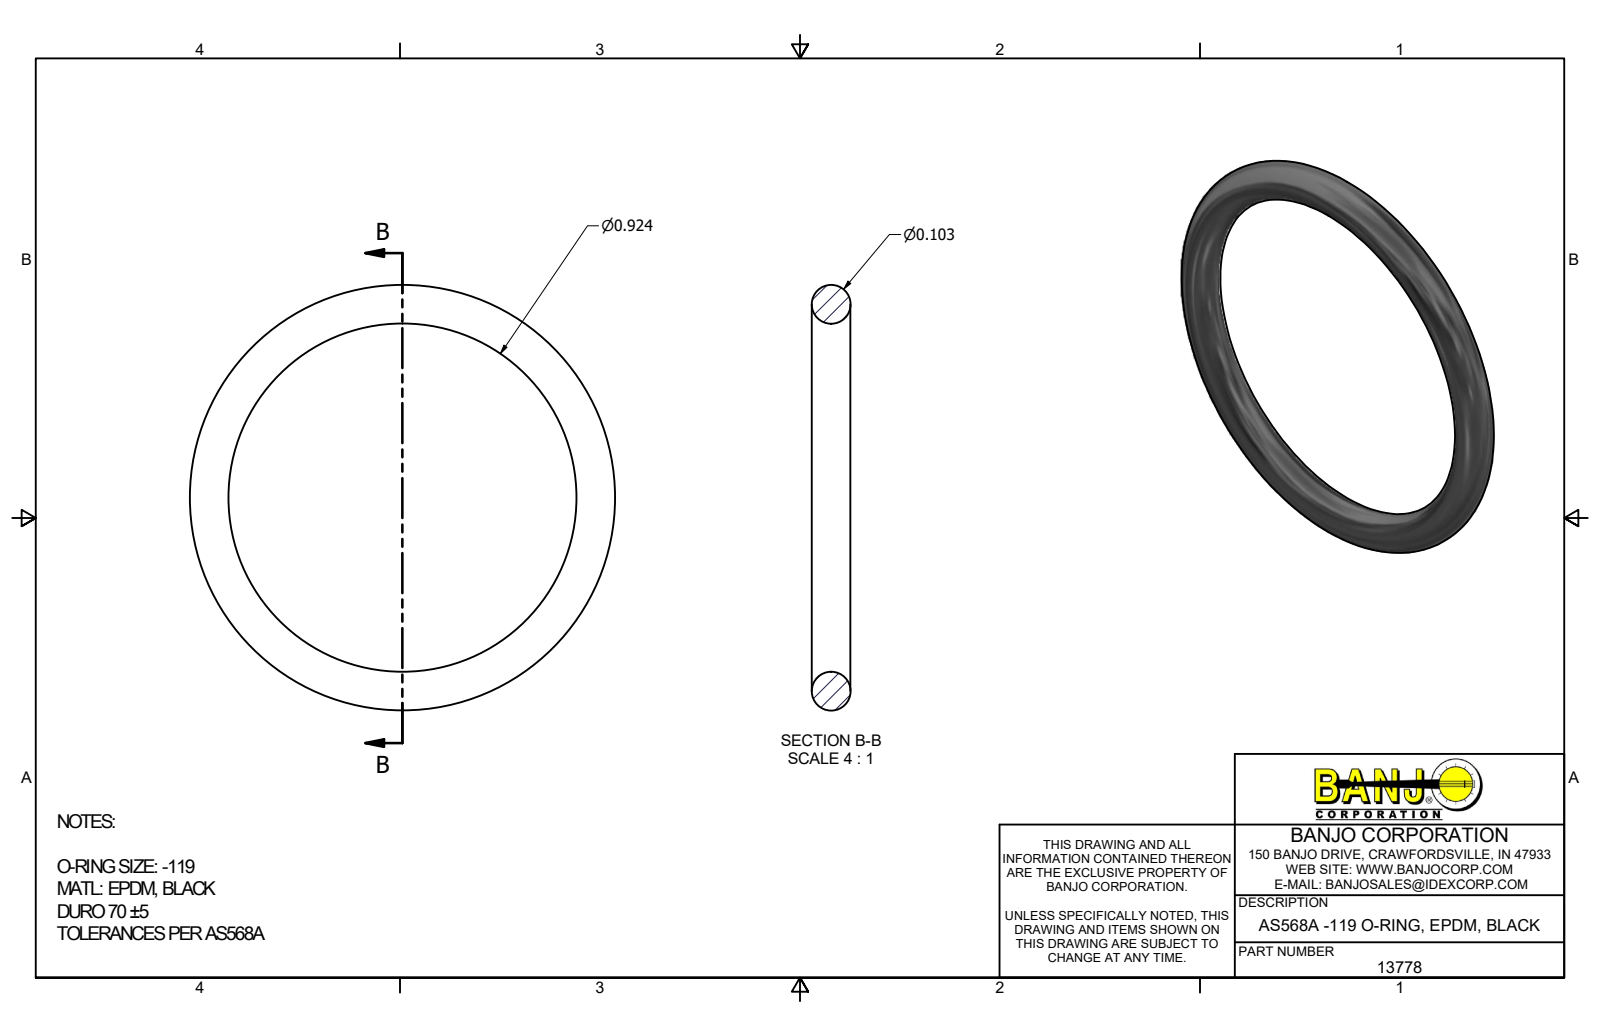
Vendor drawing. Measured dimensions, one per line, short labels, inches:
name: 13778
written by: Autodesk Inventor 2019 (AUTOMOTIVE_DESIGN)
unit: in
bodies: 1 solid, 1 faces (0 planar, 0 cylindrical, 1 other)
size: 1.13 × 1.13 × 0.103
volume: 0.027 in³; area: 1.044 in²
